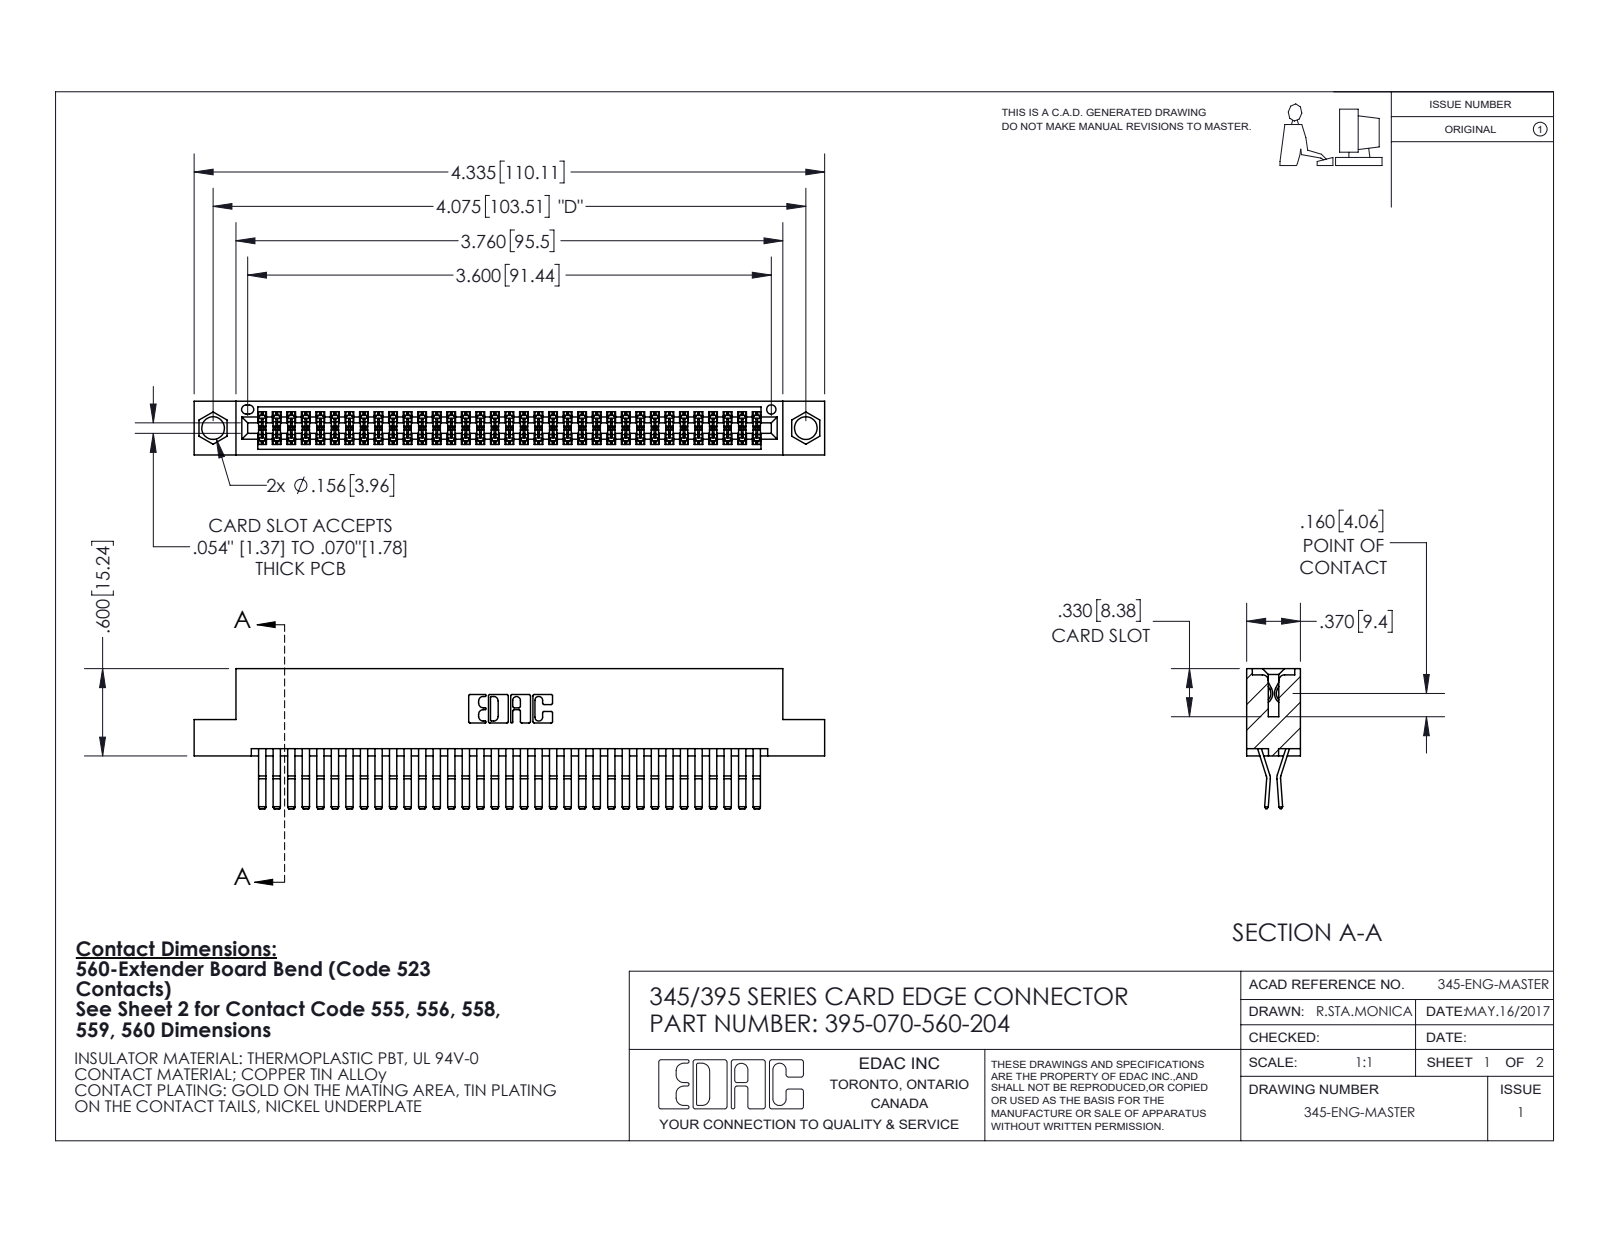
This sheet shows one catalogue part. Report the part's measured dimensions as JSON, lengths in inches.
{"part_name": "395-070-560-204; 345-292-001_560 Tail; 345 Part_Flush Mounting Lugs - 0.156 Dia-TI", "step_written_by": "SolidWorks 2020 (CONFIG_CONTROL_DESIGN)", "units": "inches", "bodies": {"solids": 71, "faces": 3780, "planar": 2404, "cylindrical": 1376, "other": 0}, "overall_size": [4.335, 0.962, 0.37], "volume_in3": 0.67, "surface_area_in2": 26.56, "round_holes": [[0.156, 2], [0.064, 1]], "partial_cylinders_radius": [[0.006, 105], [0.01, 22], [0.007, 6], [0.031, 6], [0.026, 3], [0.01, 2], [0.014, 2], [0.019, 2]], "face_to_face_distances": [0.025, 0.298, 0.072, 0.37, 0.2, 0.098, 0.272, 0.225, 0.175, 0.149], "hole_center_spacings": [0.27, 3.839, 4.075]}
